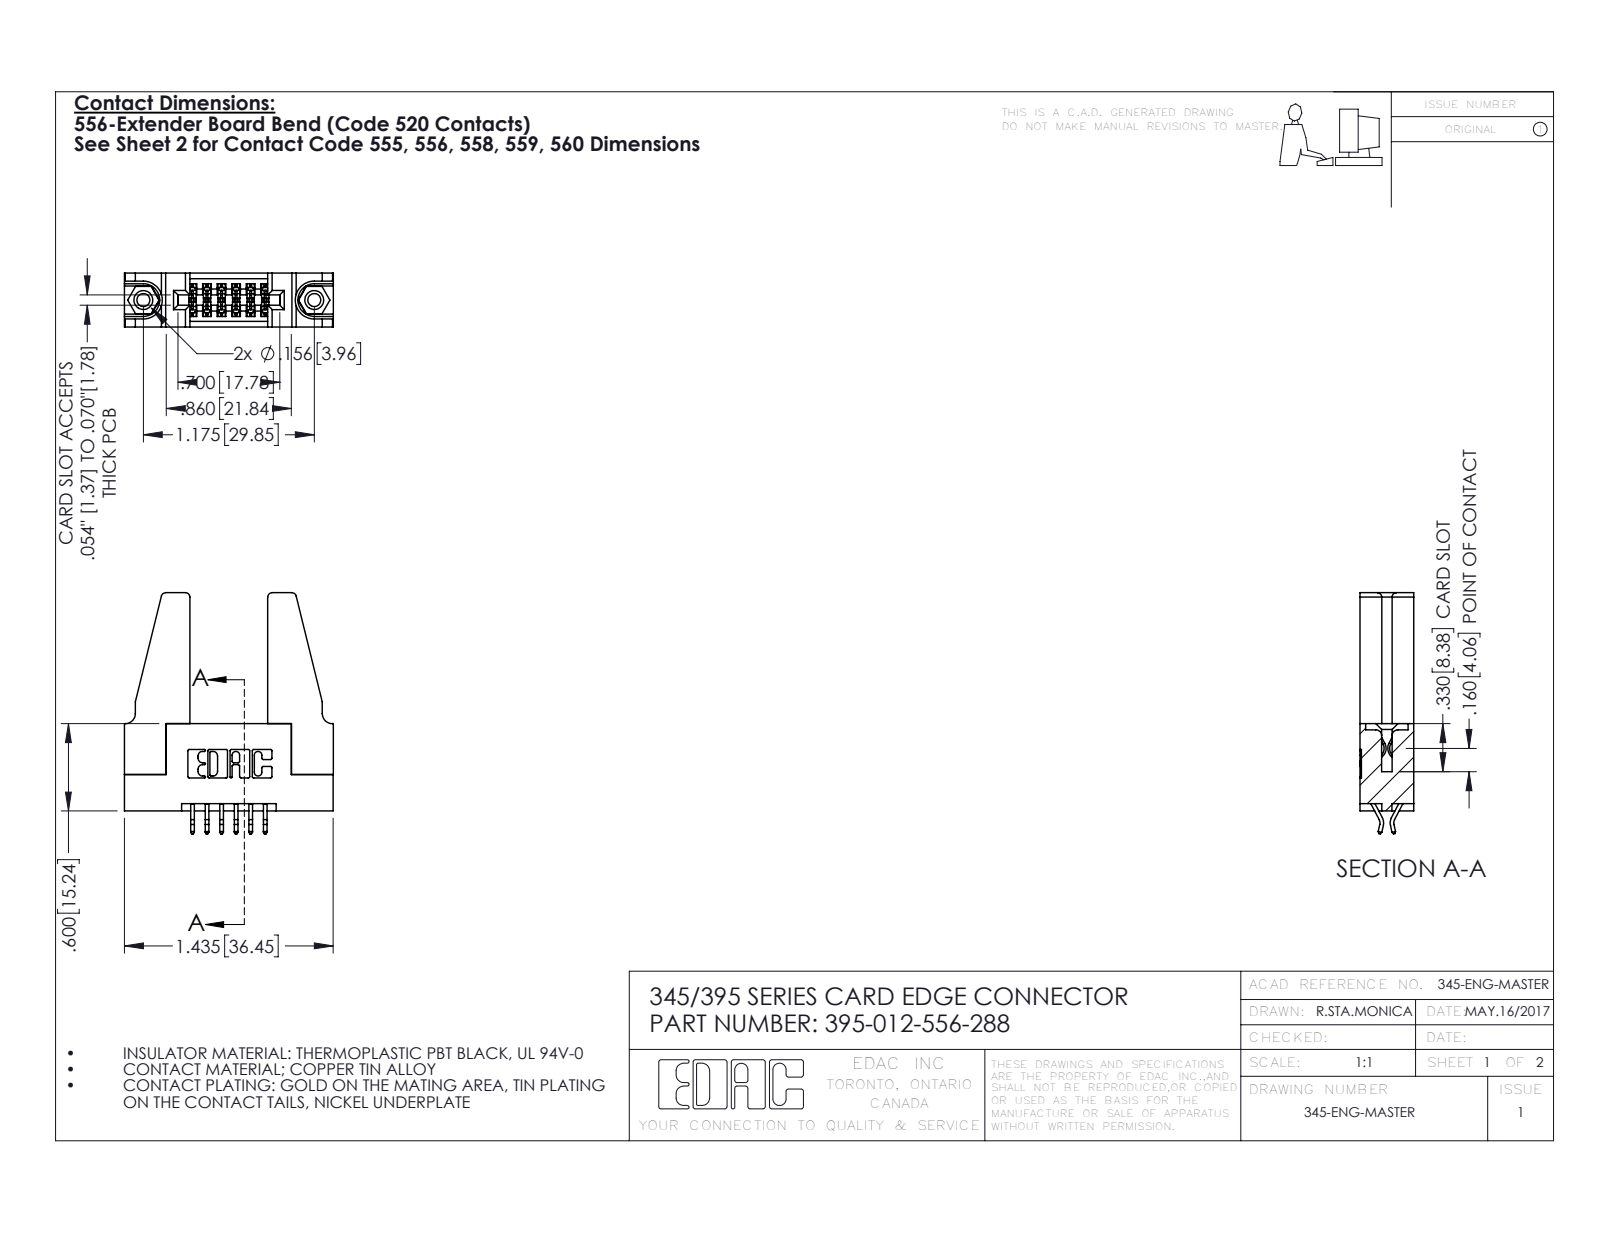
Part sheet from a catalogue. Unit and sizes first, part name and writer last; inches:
Units: inches
Overall size (bounding box): 1.657 × 1.436 × 0.37
Round holes (diameter × count): ⌀0.089 ×2, ⌀0.125 ×2, ⌀0.156 ×2, ⌀0.064 ×1
Round bosses / shafts (diameter × count): ⌀0.155 ×2
Partial cylindrical surfaces — rounded edges, fillets, slot ends (radius × count): R0.01 ×22, R0.006 ×18, R0.03 ×8, R0.007 ×6, R0.031 ×6, R0.026 ×3, R0.01 ×2, R0.014 ×2
Main face-to-face distances: 0.37, 0.072, 0.2, 0.298, 0.698, 0.15, 0.148, 0.35, 0.225, 0.025
Hole centre spacings: 0.27, 0.946, 1.175
Volume: 0.394 in³ · Surface area: 11.09 in²
Bodies: 17 solids, 922 faces (596 planar, 310 cylindrical, 16 other)
Part name (STEP PRODUCT): 395-012-556-288; 345-220-078_345-220-088; 345-292-001_556 Tail; 345 Part_Flush Mounting Lugs - 0.156 Dia-TH (+1 more)
STEP written by: SolidWorks 2016 (CONFIG_CONTROL_DESIGN)
